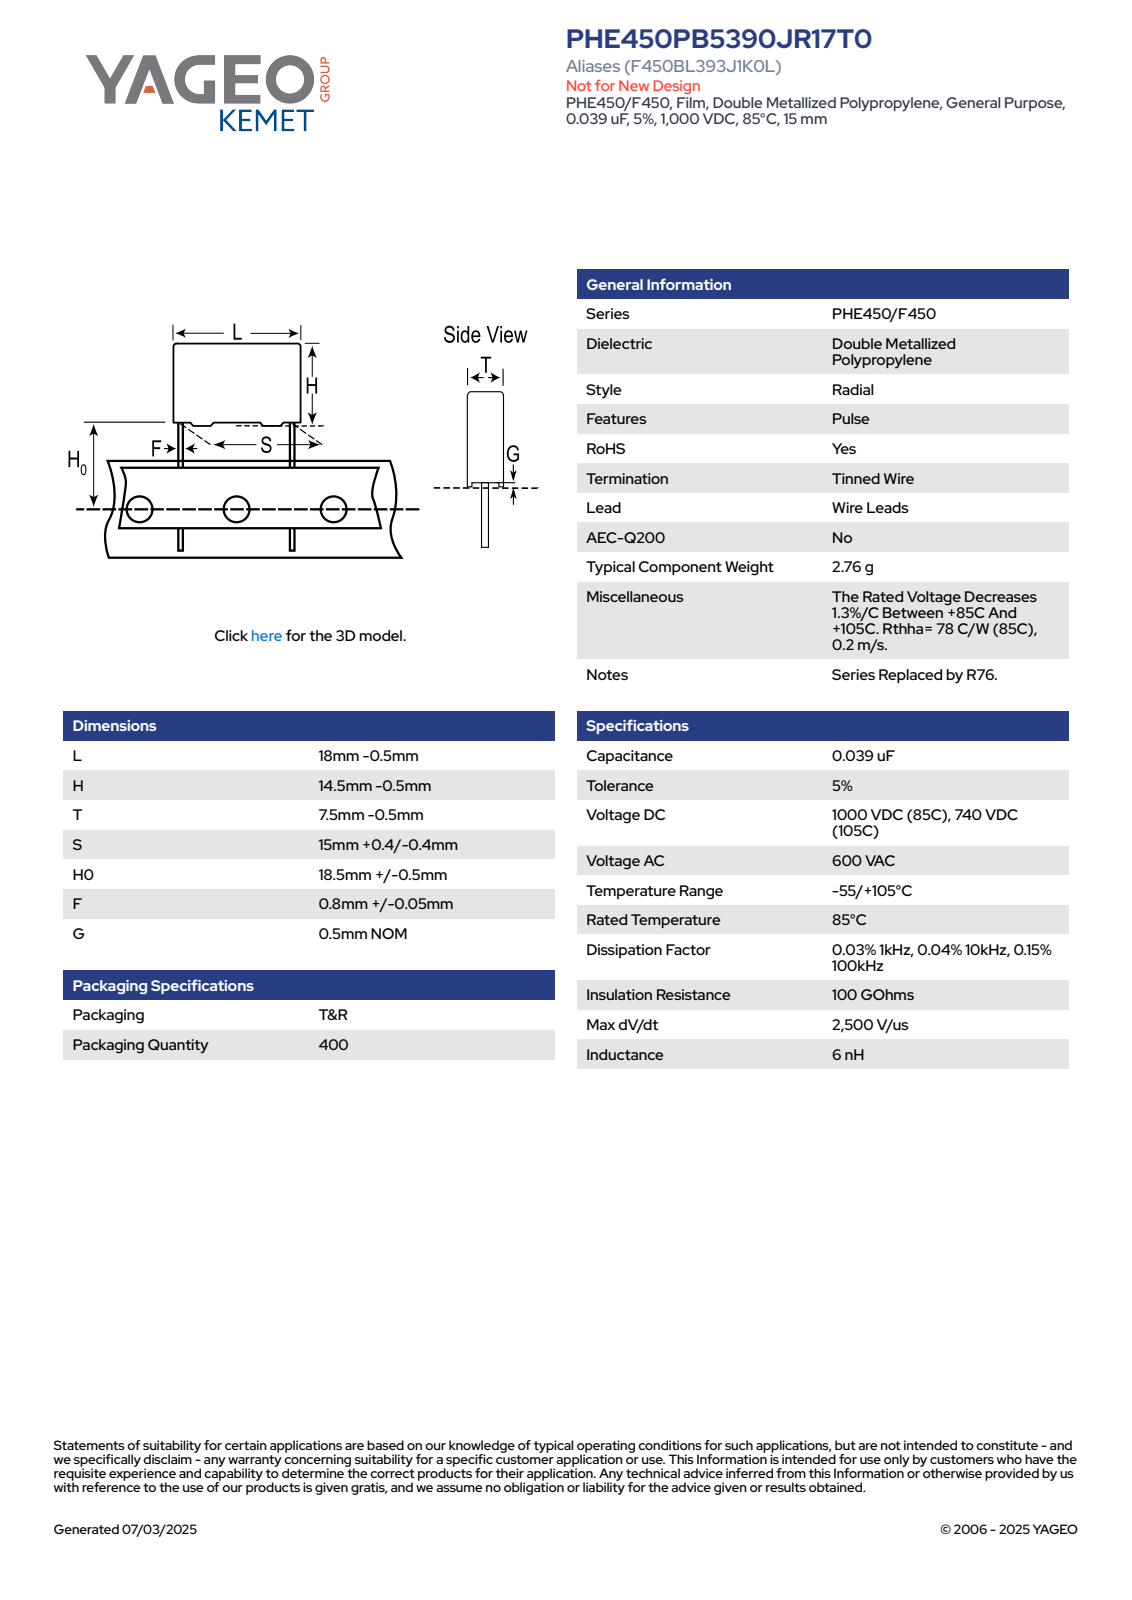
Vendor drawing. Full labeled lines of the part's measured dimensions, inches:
Part name (STEP PRODUCT): CFR_RBG_18X14.5X7.5_L17.5H14T7S15H019F0.85G0.5
STEP written by: SolidWorks 2014 (AUTOMOTIVE_DESIGN)
Units: inches
Bodies: 4 solids, 89 faces (81 planar, 8 cylindrical, 0 other)
Overall size (bounding box): 1.299 × 0.689 × 0.276
Volume: 0.102 in³ · Surface area: 1.621 in²
Round bosses / shafts (diameter × count): ⌀0.033 ×2
Partial cylindrical surfaces — rounded edges, fillets, slot ends (radius × count): R0.02 ×4
Main face-to-face distances: 0.276, 0.531, 0.689, 0.016, 0.26, 0.02, 0.551, 0.244, 0.748, 0.768
